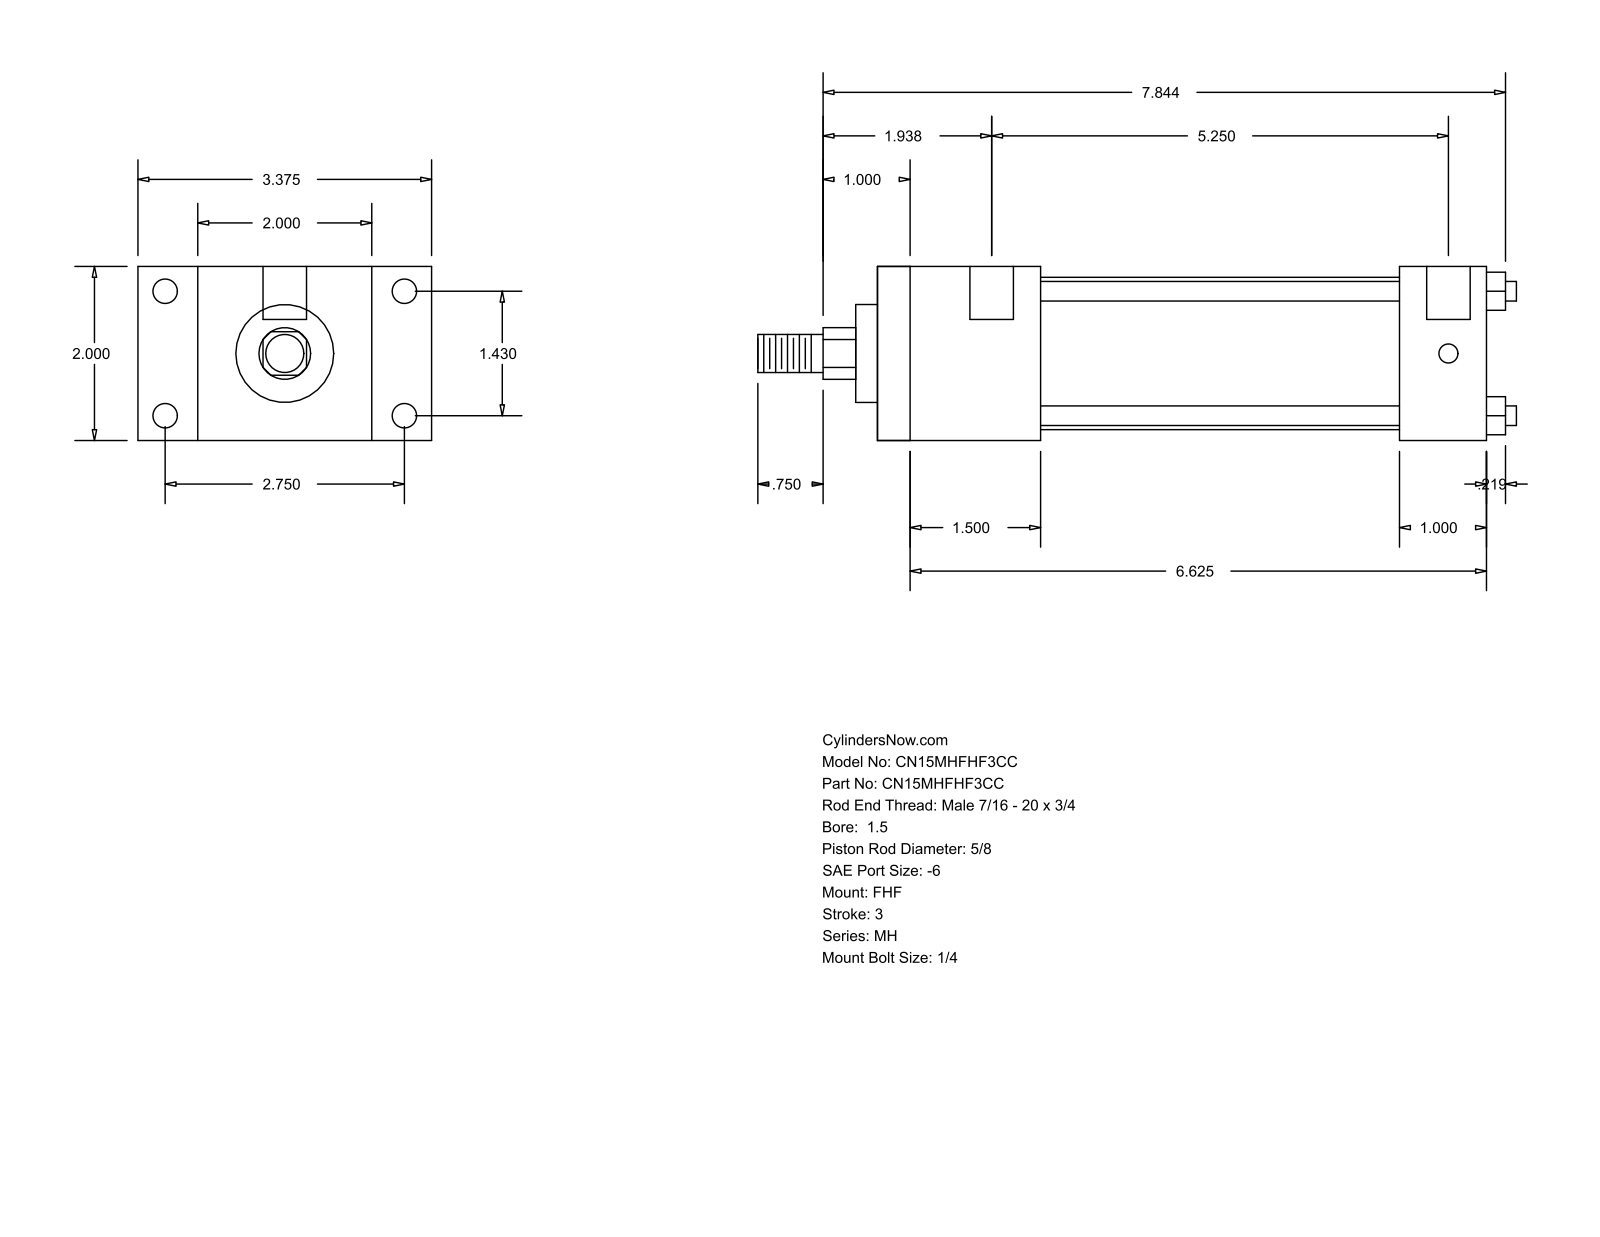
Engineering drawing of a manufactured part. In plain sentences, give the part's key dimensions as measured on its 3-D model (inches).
The part is named "MH_FHF__0150_0.625". Its 3-D file was written by "GSSL Pune (CONFIG_CONTROL_DESIGN)". It is 0 solids with 88 faces: 60 planar, 28 cylindrical and 0 other. Overall it measures 8.719 by 3.375 by 2 inches. Round holes: 4 of diameter 0.219, 4 of diameter 0.281, 2 of diameter 0.5. Round bosses or shafts: 4 of diameter 0.225, 1 of diameter 1.75, 1 of diameter 1.125, 1 of diameter 0.625, 1 of diameter 0.437. Partial cylindrical surfaces (rounded edges, fillets, slot ends): 1 of radius 0.297. The main face-to-face distances are 2, 0.687, 2.687, 1.875, 3.375, 7, 5.125, 1, 6, 4.125. The hole center spacings are 1.43, 2.75, 3.099, 5.375, 0.125, 5.25.
